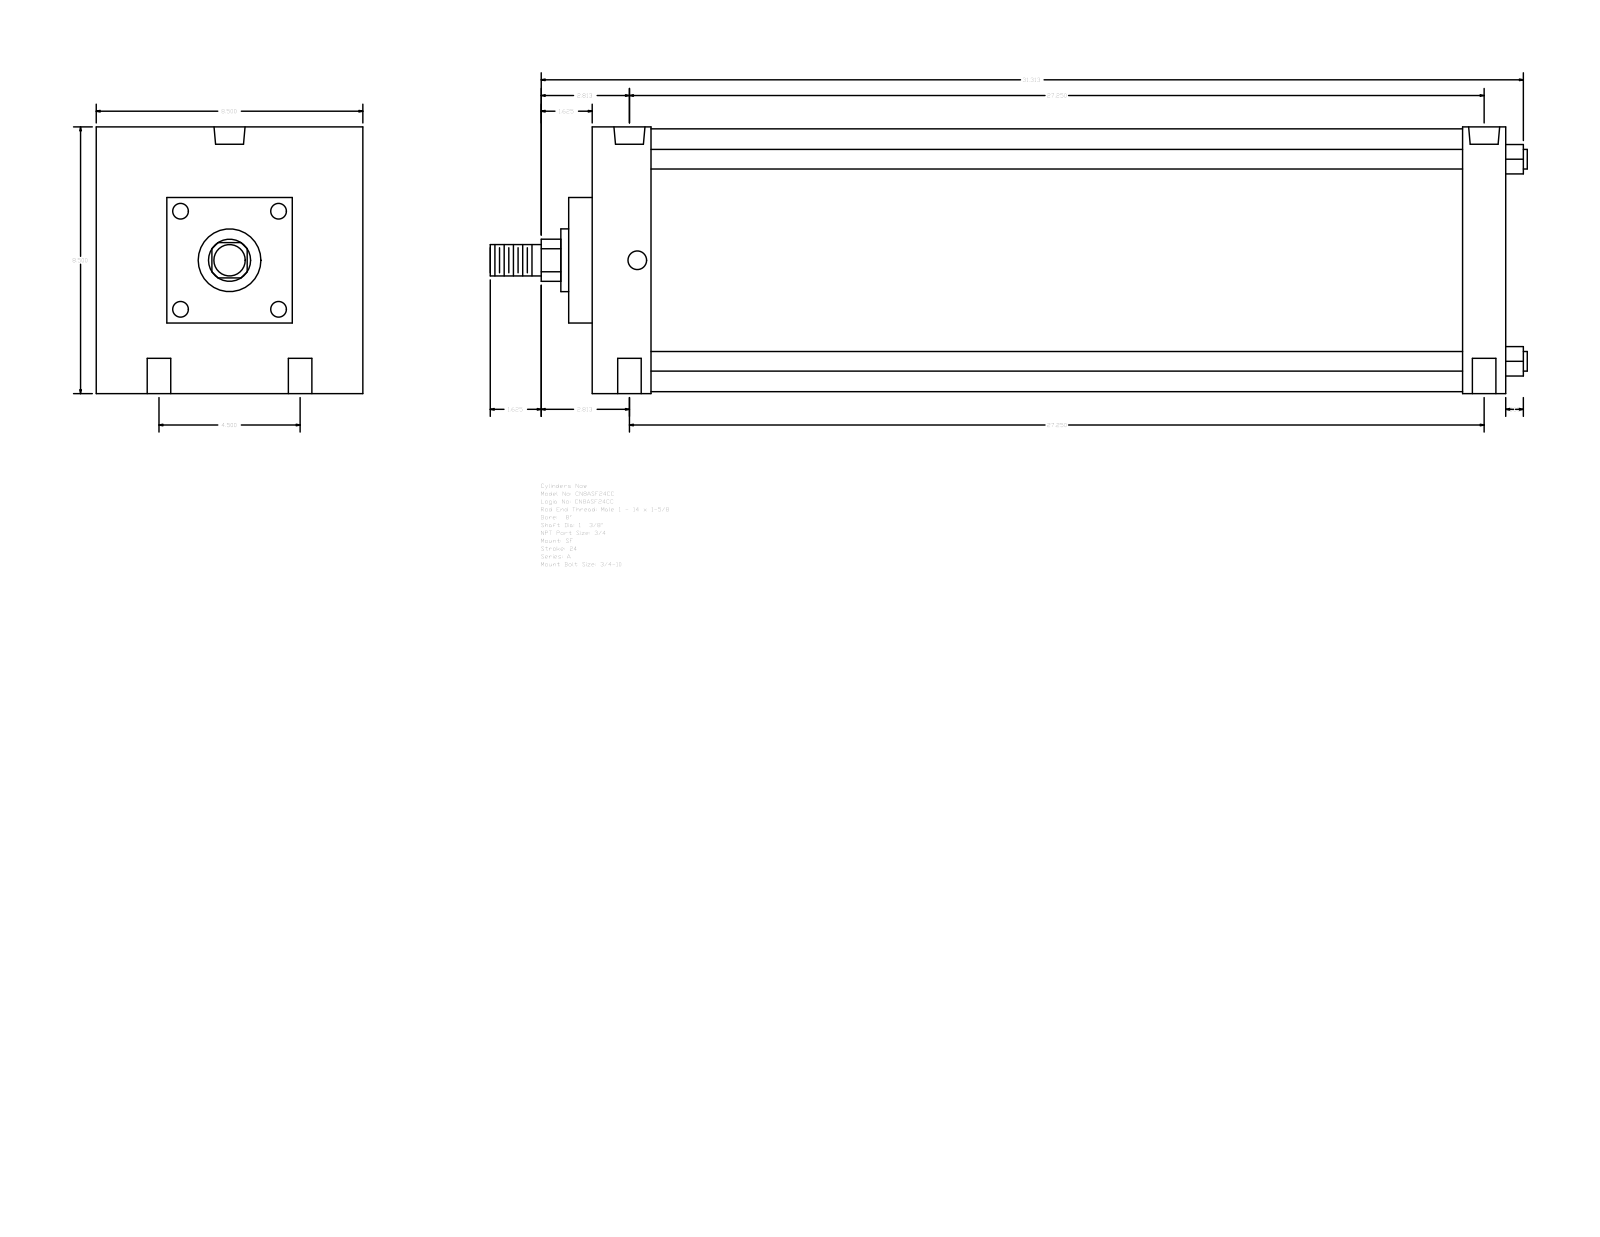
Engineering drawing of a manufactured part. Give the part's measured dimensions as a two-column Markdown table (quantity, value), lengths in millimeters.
| quantity | value |
| --- | --- |
| part name | A_SF__0800_1.375 |
| STEP written by | GSSL Pune (CONFIG_CONTROL_DESIGN) |
| units | millimeters |
| bodies | 0 solids, 93 faces (67 planar, 26 cylindrical, 0 other) |
| overall size | 839.79 × 215.9 × 215.9 |
| round holes (diameter × count) | 19.05 × 4, 15.08 × 2, 25.12 × 2 |
| round bosses / shafts (diameter × count) | 15.88 × 4, 212.72 × 1, 50.8 × 1, 34.92 × 1, 25.4 × 1 |
| partial cylindrical surfaces (radius × count) | 17.06 × 1 |
| main face-to-face distances | 739.78, 215.9, 47.63, 704.85, 657.22, 692.15, 34.93, 19.04, 66.67, 723.89 |
| hole center spacings | 57.15, 694.51, 692.15, 114.3, 701.52, 679.45 |
